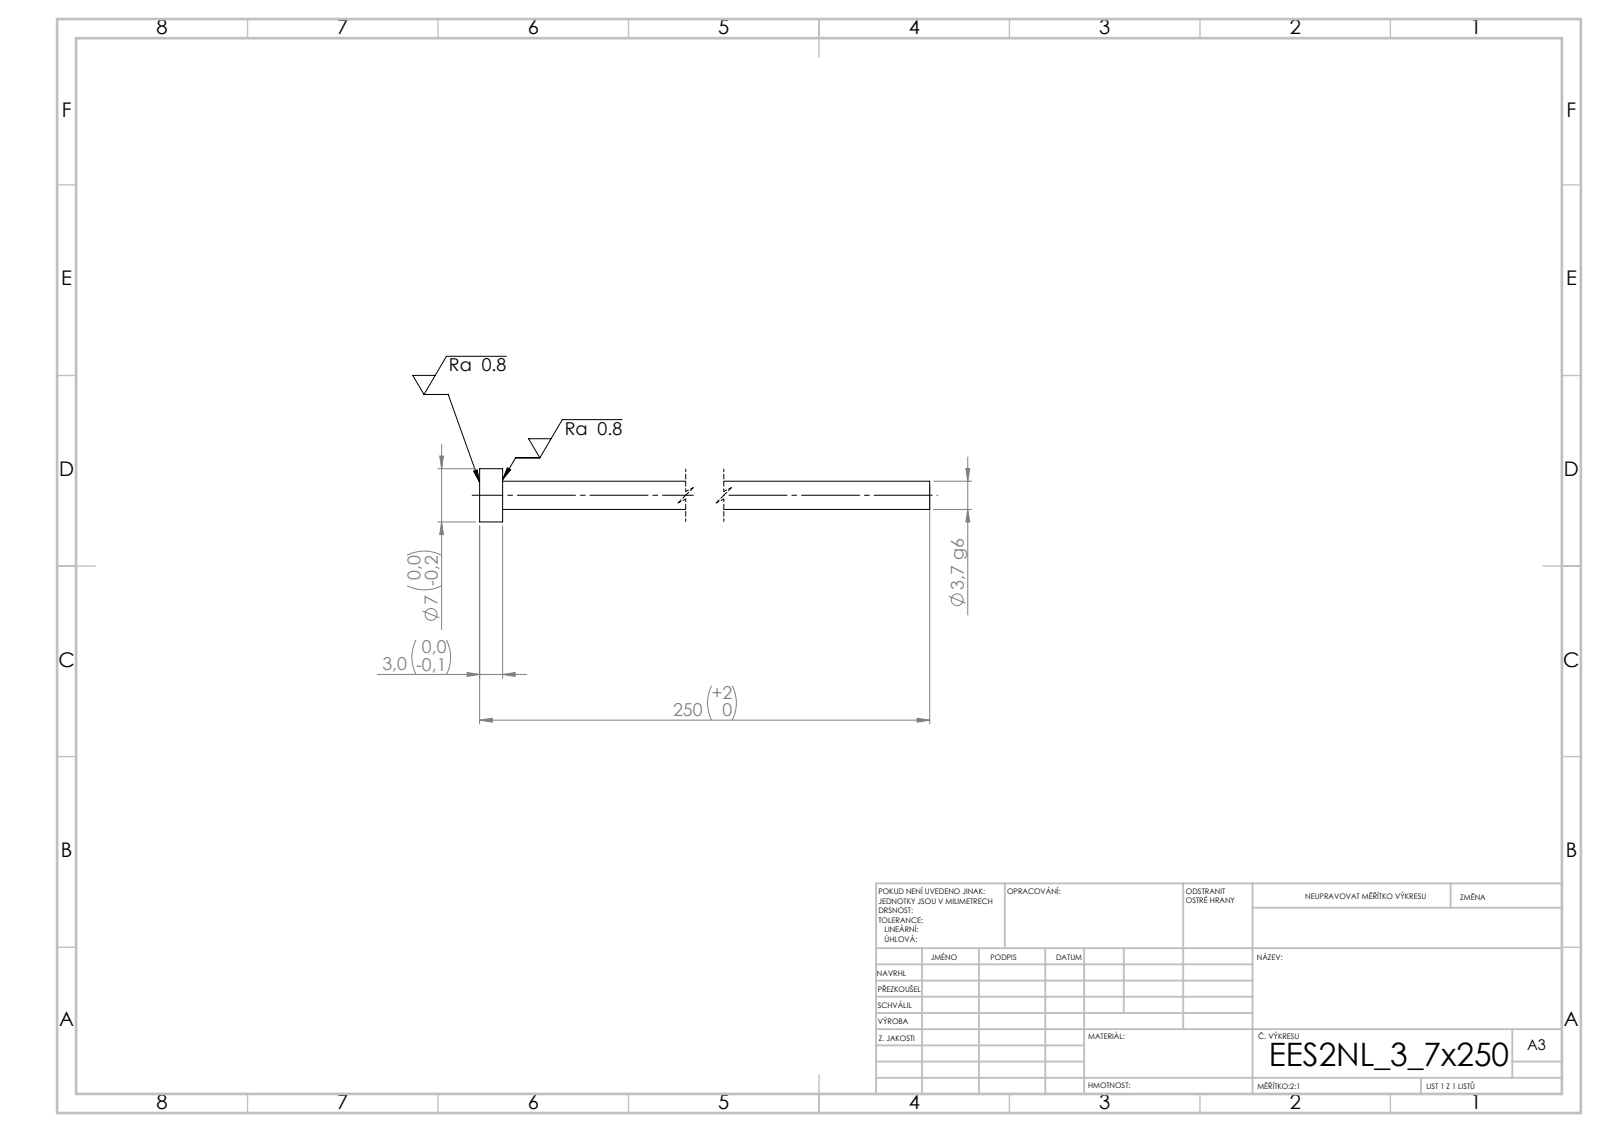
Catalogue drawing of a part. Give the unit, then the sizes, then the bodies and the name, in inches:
Units: inches
Overall size (bounding box): 9.843 × 0.276 × 0.276
Round bosses / shafts (diameter × count): ⌀0.276 ×1, ⌀0.146 ×1
Main face-to-face distances: 0.118, 9.843, 9.724
Volume: 0.169 in³ · Surface area: 4.672 in²
Bodies: 1 solid, 7 faces (3 planar, 4 cylindrical, 0 other)
STEP written by: SolidWorks 2019 (CONFIG_CONTROL_DESIGN)
